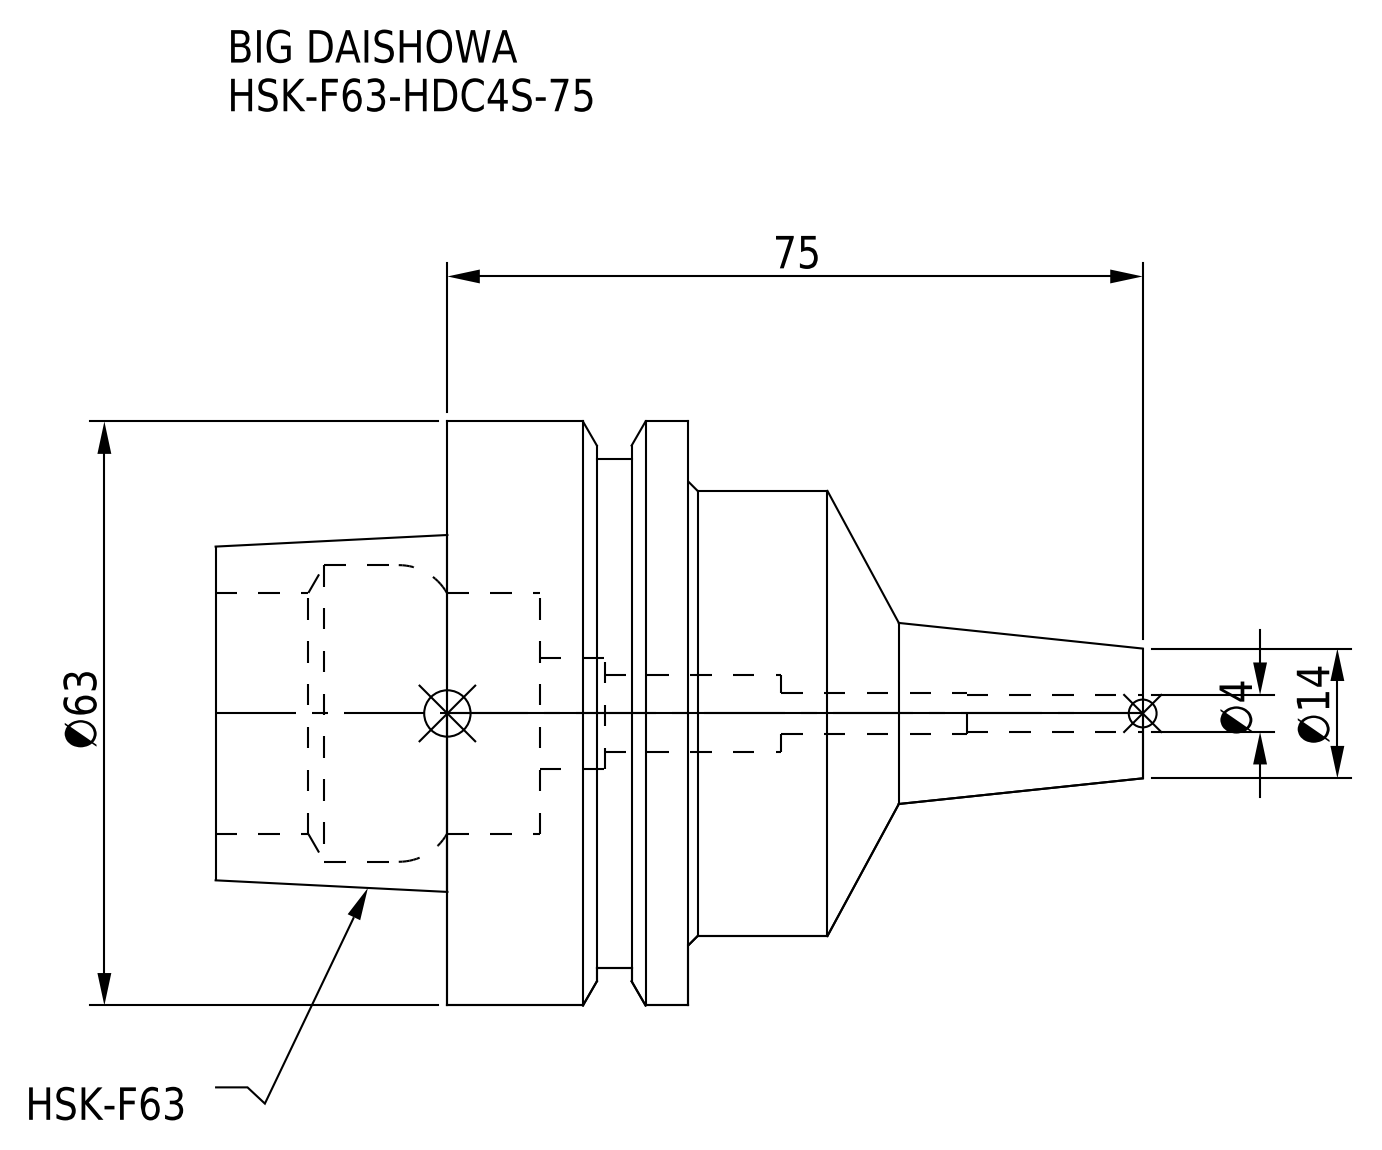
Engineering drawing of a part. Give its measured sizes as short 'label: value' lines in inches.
name: HSK-F63-HDC4S-75
written by: CREO PARAMETRIC BY PTC INC, 2016380 (AUTOMOTIVE_DESIGN)
unit: in
bodies: 1 solid, 50 faces (10 planar, 24 cylindrical, 16 other)
size: 3.937 × 2.48 × 2.48
volume: 7.373 in³; area: 36.18 in²
holes: 1× ⌀0.157, 1× ⌀0.177, 1× ⌀0.325, 1× ⌀0.472, 1× ⌀1.024, 1× ⌀1.26
bosses: 1× ⌀2.48, 1× ⌀2.165, 1× ⌀1.89
face distances: 1.024, 2.008, 0.984, 0.632, 0.392, 1.376, 0.783, 0.635, 0.241, 0.391
